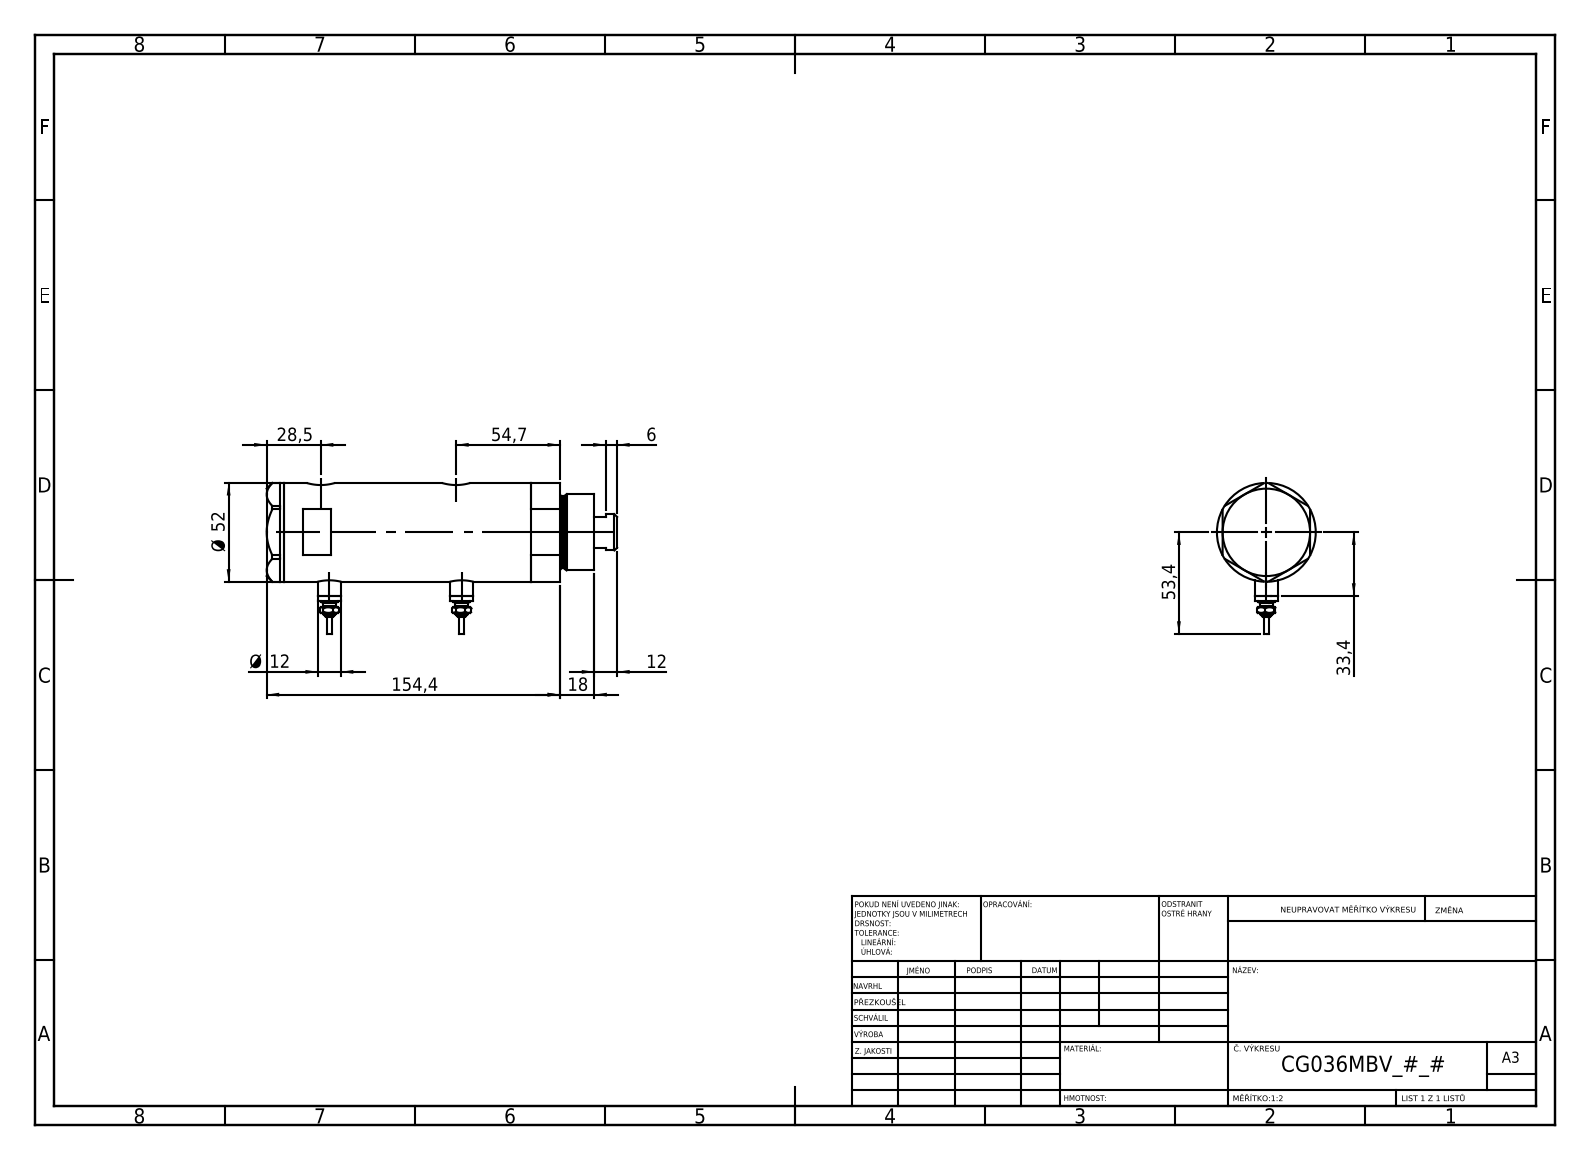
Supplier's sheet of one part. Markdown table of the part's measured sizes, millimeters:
| quantity | value |
| --- | --- |
| part name | Switch; V270CG_VC; V270CG_BACK; V270CG_MIDDLE (+1 more) |
| STEP written by | SolidWorks 2019 (CONFIG_CONTROL_DESIGN) |
| units | millimeters |
| bodies | 6 solids, 223 faces (92 planar, 67 cylindrical, 64 other) |
| overall size | 184.4 × 79.4 × 52 |
| volume | 317 254 mm³ |
| surface area | 80 412 mm² |
| round holes (diameter × count) | 9.64 × 2, 12.5 × 2, 15 × 2, 6.5 × 1, 20 × 1, 21.5 × 1, 36 × 1, 44 × 1 |
| round bosses / shafts (diameter × count) | 12 × 2, 9 × 2, 7 × 2, 4.5 × 2, 2.5 × 2, 52 × 1, 40 × 1, 38 × 1 |
| main face-to-face distances | 23.8, 9, 93.5, 69.7, 32.8, 102.5, 46, 138.9, 129.9, 106.1 |
| hole center spacings | 2.9, 4.5, 66.7, 69.6, 71.2, 74.1 |
